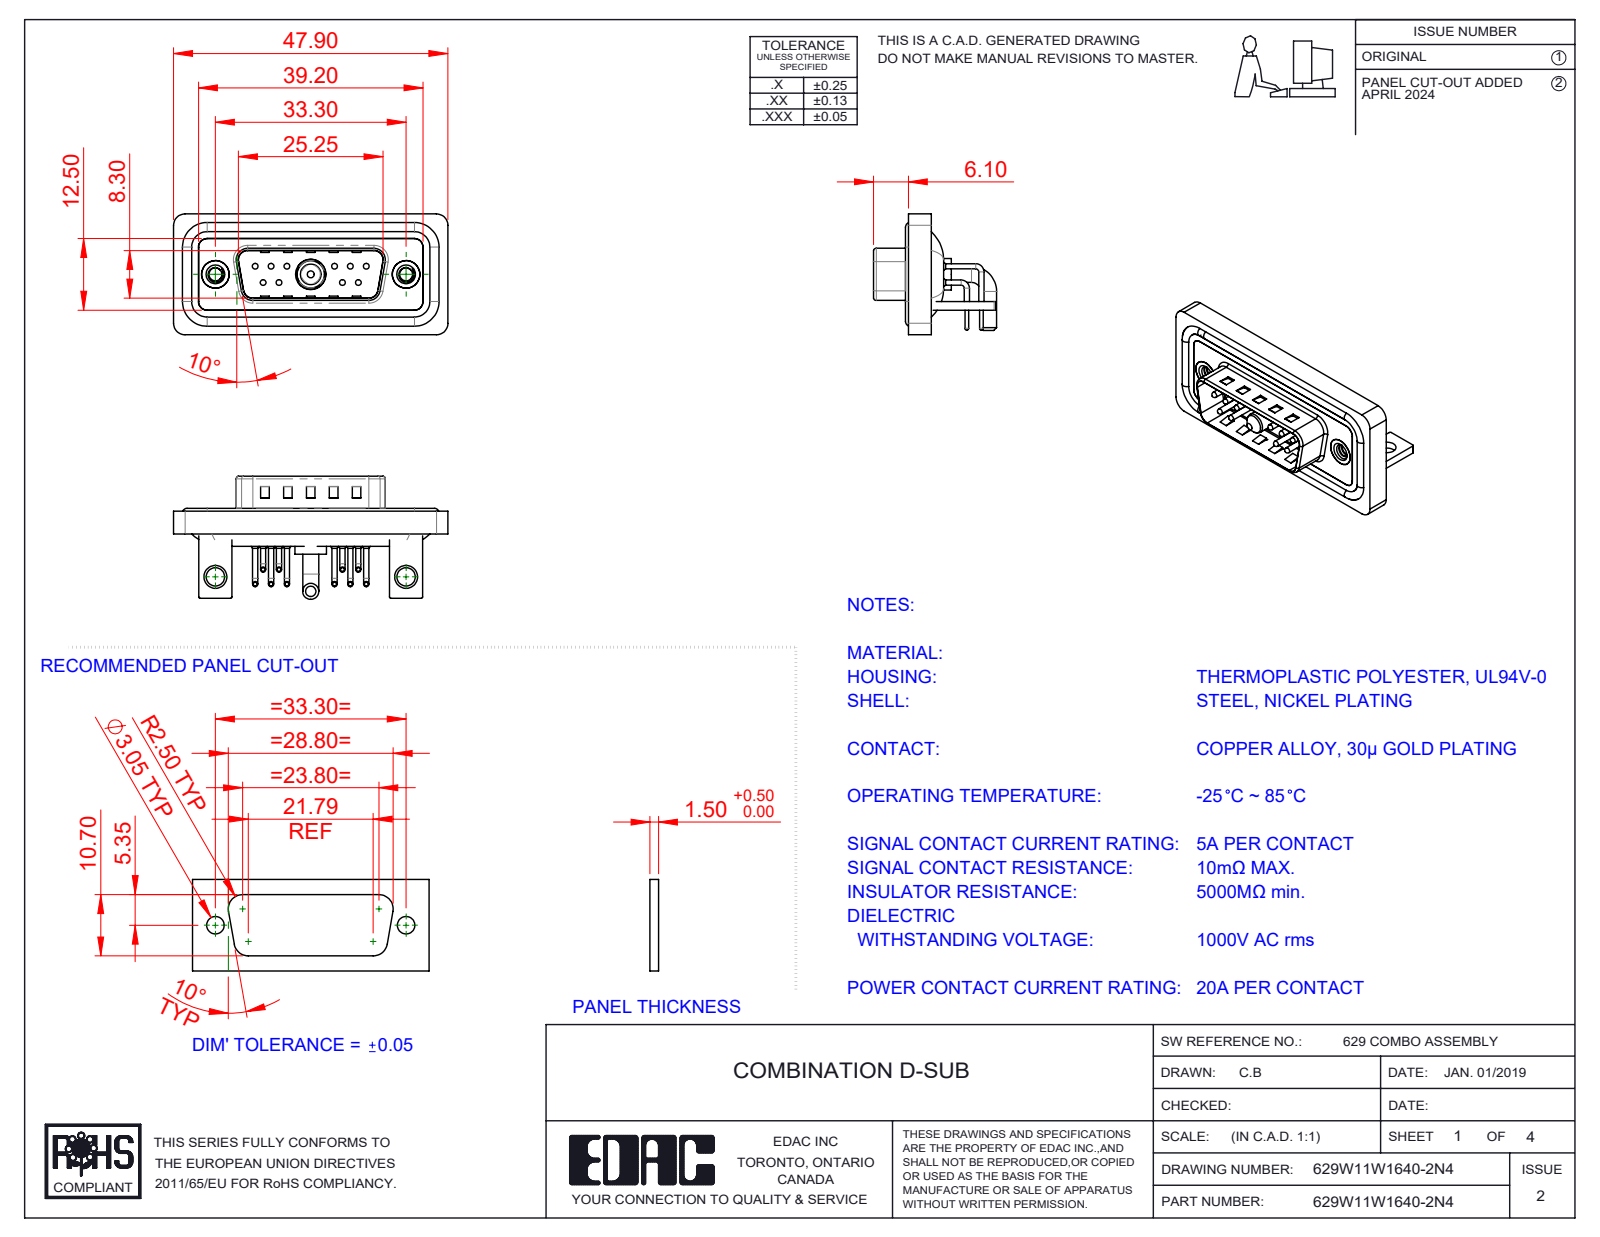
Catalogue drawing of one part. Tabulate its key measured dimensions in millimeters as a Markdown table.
| quantity | value |
| --- | --- |
| part name | 629W11W1640-2N4; Power Pin_20A RA; 629Combo Threaded Rivet_3; 629Combo Housing_11W1 (+6 more) |
| STEP written by | SolidWorks 2023 (CONFIG_CONTROL_DESIGN) |
| units | millimeters |
| bodies | 21 solids, 1643 faces (856 planar, 587 cylindrical, 200 other) |
| overall size | 47.9 × 21.5 × 21.1 |
| volume | 5 867 mm³ |
| surface area | 9 867 mm² |
| round holes (diameter × count) | 0.75 × 10, 1.6 × 10, 2 × 10, 2.26 × 2, 3.2 × 2, 4 × 2, 4.8 × 2, 5 × 2, 4.85 × 1, 5.3 × 1 |
| round bosses / shafts (diameter × count) | 0.9 × 20, 1.5 × 10, 1 × 10, 0.65 × 10, 1.6 × 4, 4.9 × 2, 2.8 × 2, 5.5 × 1 |
| partial cylindrical surfaces (radius × count) | 2 × 21, 1.5 × 18, 0.25 × 16, 1.01 × 10, 0.5 × 9, 1.6 × 8, 1 × 7, 0.6 × 4 |
| main face-to-face distances | 0.4, 0.8, 1.5, 2.9, 2.1, 1.1, 1.6, 1.2, 3.7, 4.1 |
| hole center spacings | 3.16, 2.77, 13.85, 11.08, 16.62, 5.03, 5.04, 5.54 |
